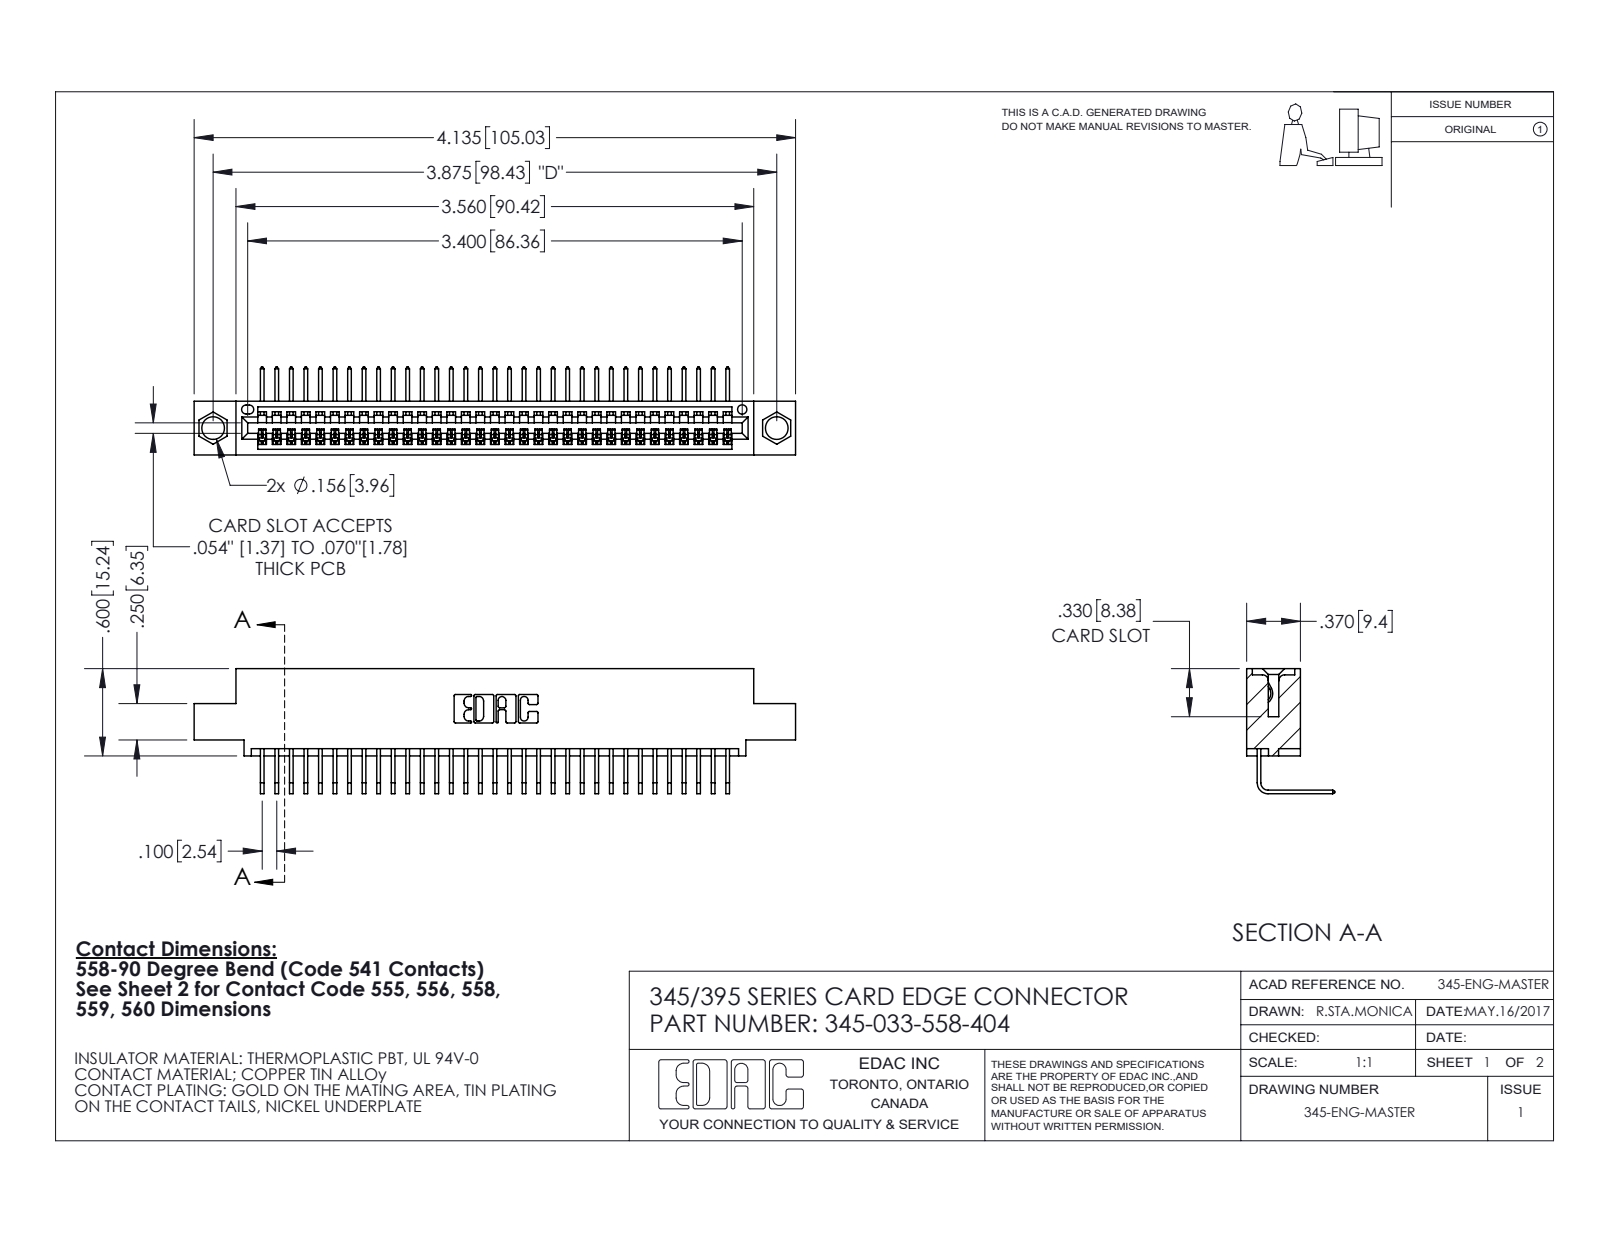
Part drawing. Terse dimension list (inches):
name: 345-292-001_558 Tail - 2; 345-033-558-404; 345 Part_0.110 Offset - 0.156 Dia-TI
written by: SolidWorks 2020 (CONFIG_CONTROL_DESIGN)
unit: in
bodies: 34 solids, 2124 faces (1484 planar, 640 cylindrical, 0 other)
size: 4.135 × 0.859 × 0.605
volume: 0.6 in³; area: 20.95 in²
holes: 2× ⌀0.156, 1× ⌀0.064
rounds: 66× R0.006, 22× R0.01, 6× R0.007, 6× R0.031, 3× R0.026, 2× R0.031, 2× R0.04, 1× R0.014
face distances: 0.072, 0.298, 0.37, 0.2, 0.098, 0.272, 0.025, 0.225, 0.149, 0.072
hole spacings: 0.27, 3.64, 3.875
